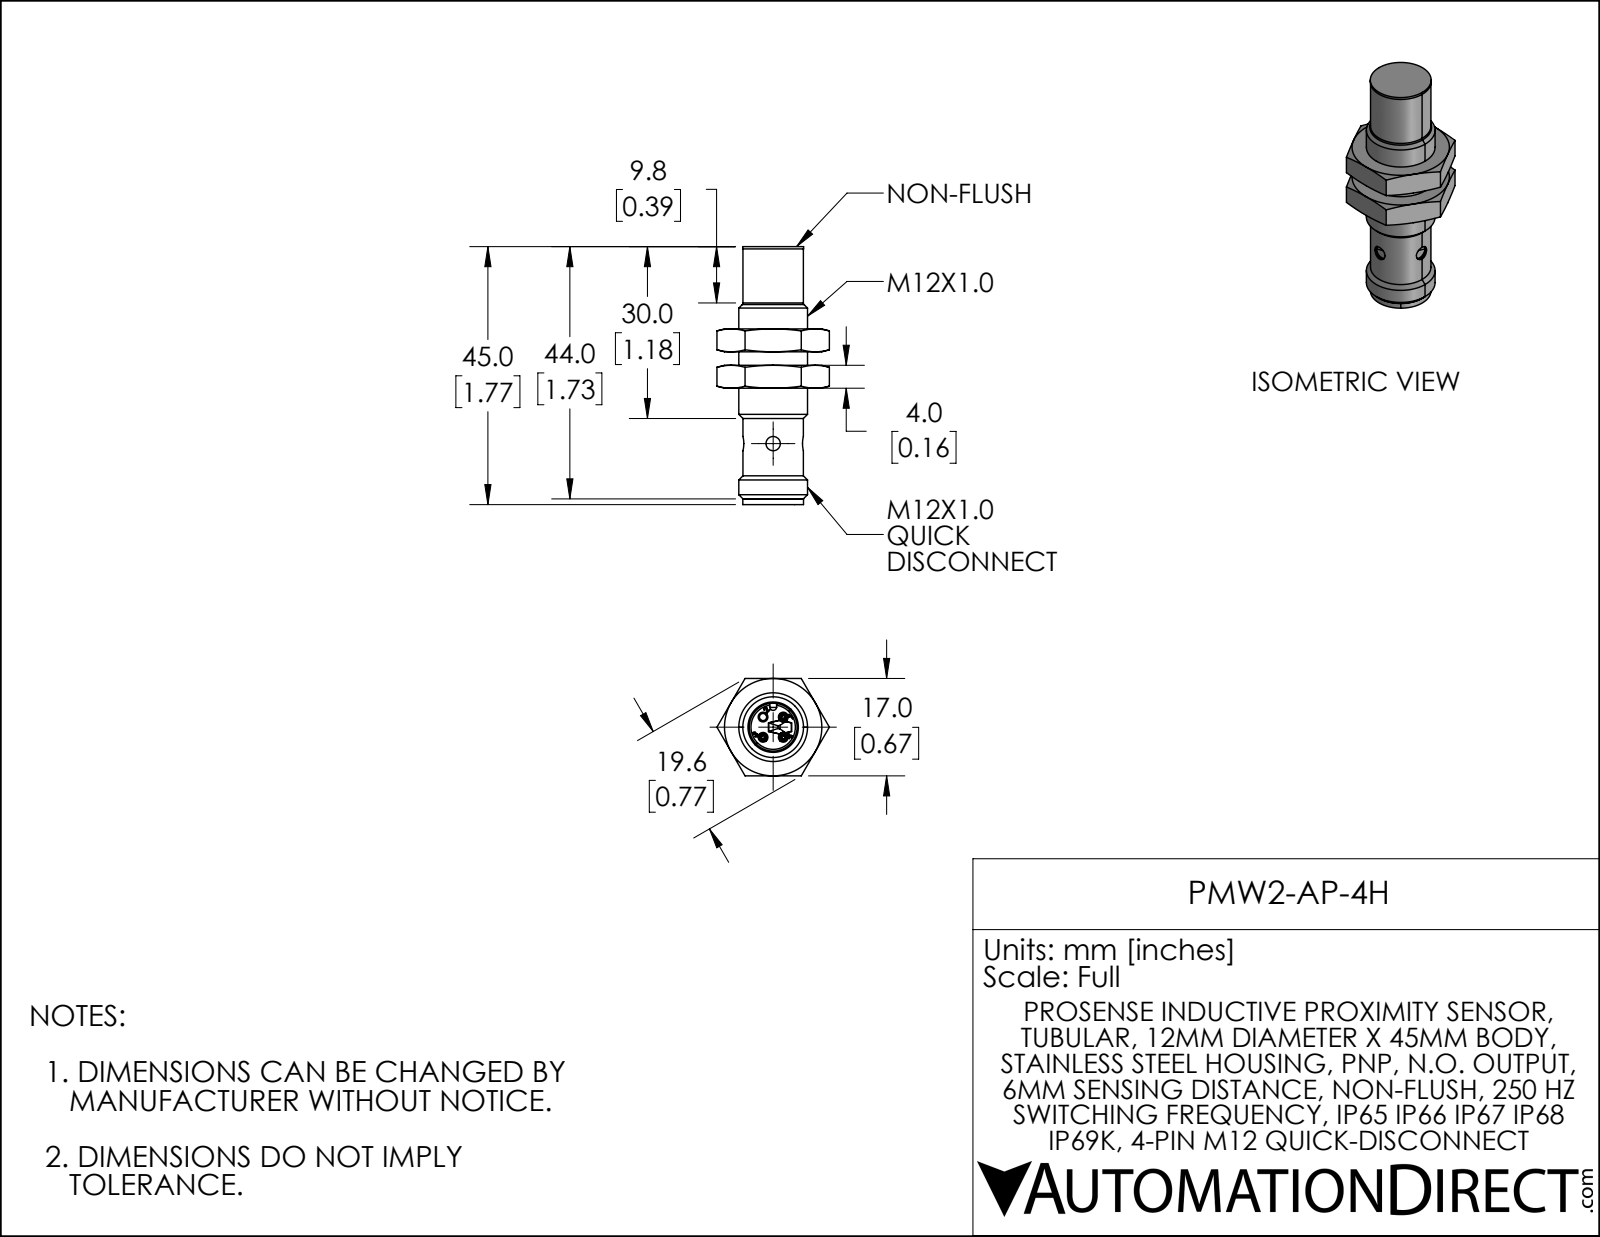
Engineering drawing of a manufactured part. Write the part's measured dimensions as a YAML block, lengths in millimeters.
part_name: "PMW2-AP-4H"
step_written_by: "SolidWorks 2019 (CONFIG_CONTROL_DESIGN)"
units: millimeters
bodies: {solids: 3, faces: 402, planar: 104, cylindrical: 104, other: 194}
overall_size: [45, 19.6, 17]
volume: 5230
surface_area: 4187
round_holes:
  - {diameter: 1, count: 3}
  - {diameter: 1.1, count: 3}
  - {diameter: 2.5, count: 2}
  - {diameter: 8.4, count: 1}
  - {diameter: 10, count: 1}
  - {diameter: 10.9, count: 1}
round_bosses_or_shafts:
  - {diameter: 1, count: 3}
  - {diameter: 12, count: 1}
  - {diameter: 10.6, count: 1}
  - {diameter: 10.6, count: 1}
  - {diameter: 10.5, count: 1}
  - {diameter: 10.5, count: 1}
  - {diameter: 9.9, count: 1}
  - {diameter: 7.6, count: 1}
partial_cylinders:
  - {radius: 0.3, count: 18}
  - {radius: 0.5, count: 3}
  - {radius: 0.5, count: 2}
  - {radius: 0.5, count: 1}
  - {radius: 0.5, count: 1}
  - {radius: 0.6, count: 1}
  - {radius: 4.1, count: 1}
face_to_face_distances: [4, 6.4, 17, 10.3, 2.4, 14.4, 18.4, 20.7, 24.7, 36.1]
hole_center_spacings: [2.5, 3.5, 5]
